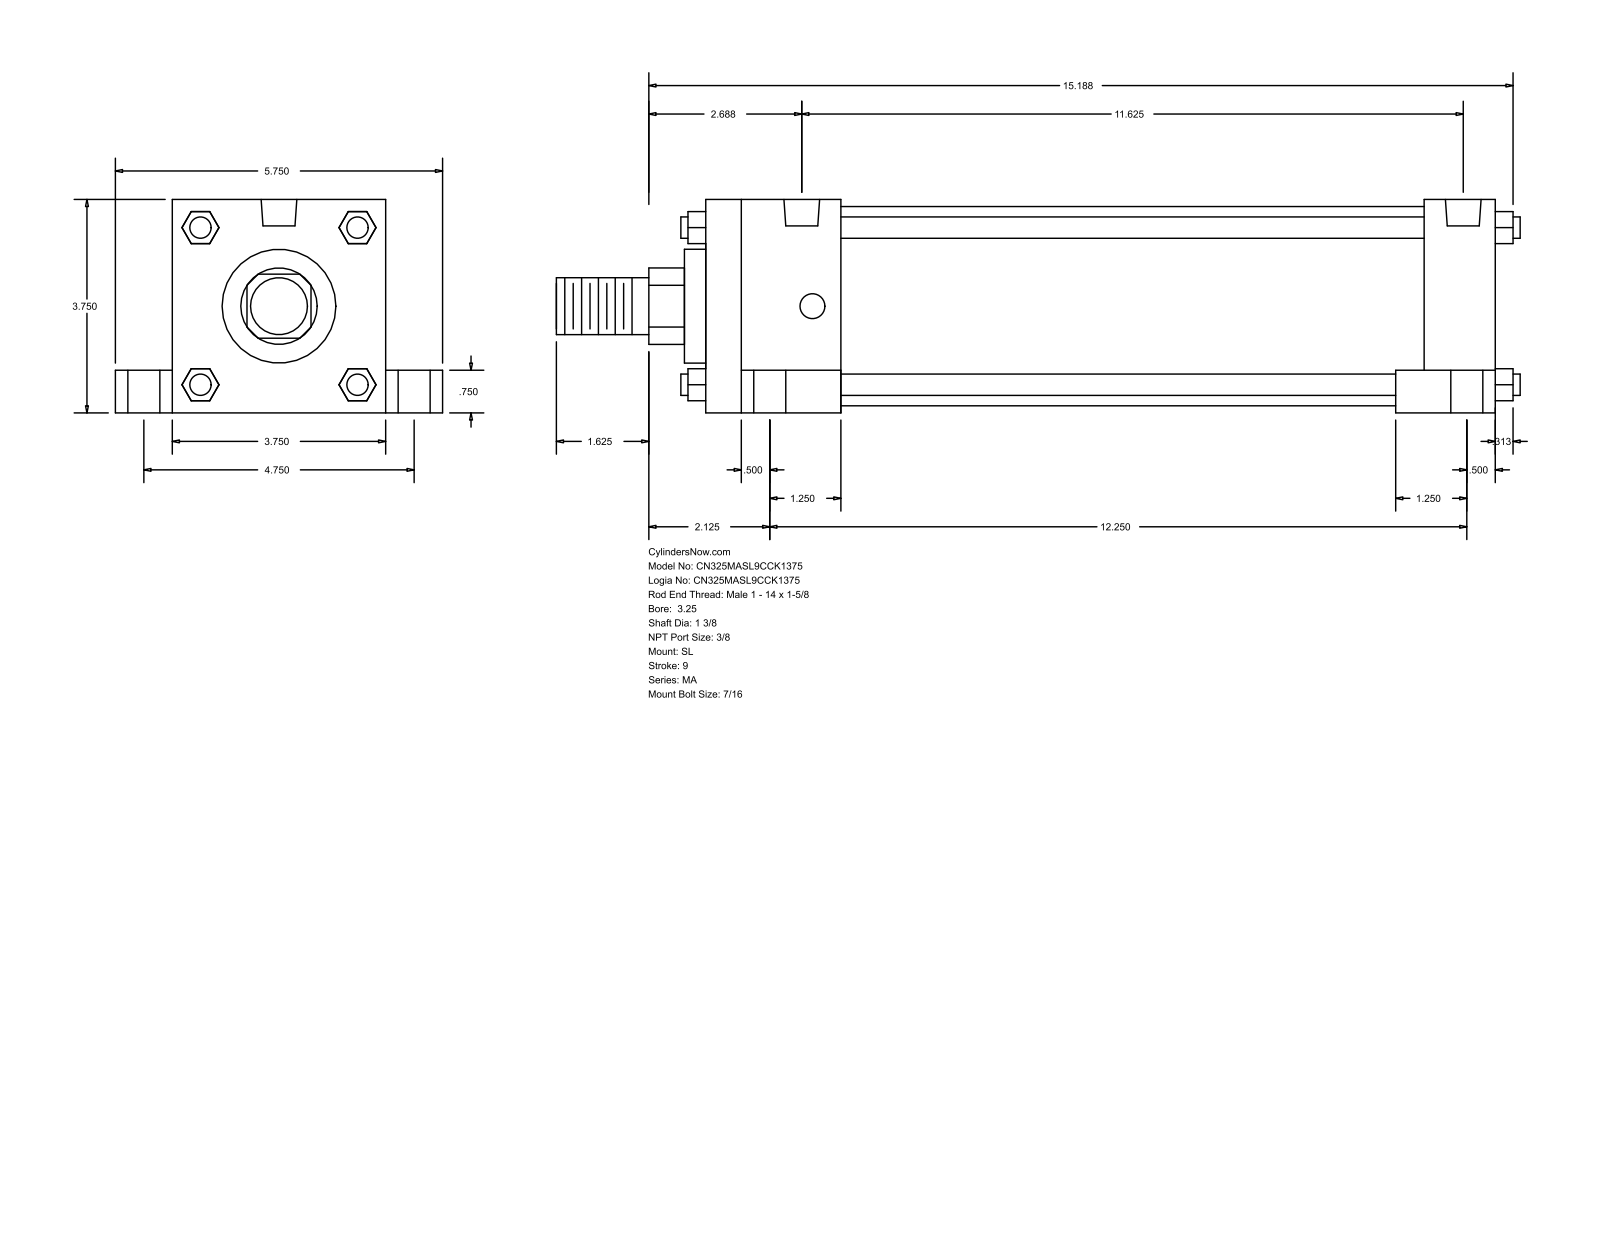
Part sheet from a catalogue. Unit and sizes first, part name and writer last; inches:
Units: inches
Overall size (bounding box): 16.937 × 5.75 × 3.75
Round holes (diameter × count): ⌀0.437 ×4, ⌀0.563 ×4, ⌀0.813 ×4, ⌀0.627 ×2
Round bosses / shafts (diameter × count): ⌀0.375 ×4, ⌀3.5 ×1, ⌀2 ×1, ⌀1.375 ×1, ⌀1 ×1
Partial cylindrical surfaces — rounded edges, fillets, slot ends (radius × count): R0.672 ×1
Main face-to-face distances: 3.75, 13.875, 10.25, 1, 4.75, 12.625, 1.25, 2.375, 11.5, 0.75
Hole centre spacings: 0.188, 2.376, 2.388, 2.441, 2.491, 4.75, 11.25, 11.437
Bodies: 0 solids, 148 faces (112 planar, 36 cylindrical, 0 other)
Part name (STEP PRODUCT): MA_SL__0325_1.375
STEP written by: GSSL Pune (CONFIG_CONTROL_DESIGN)
